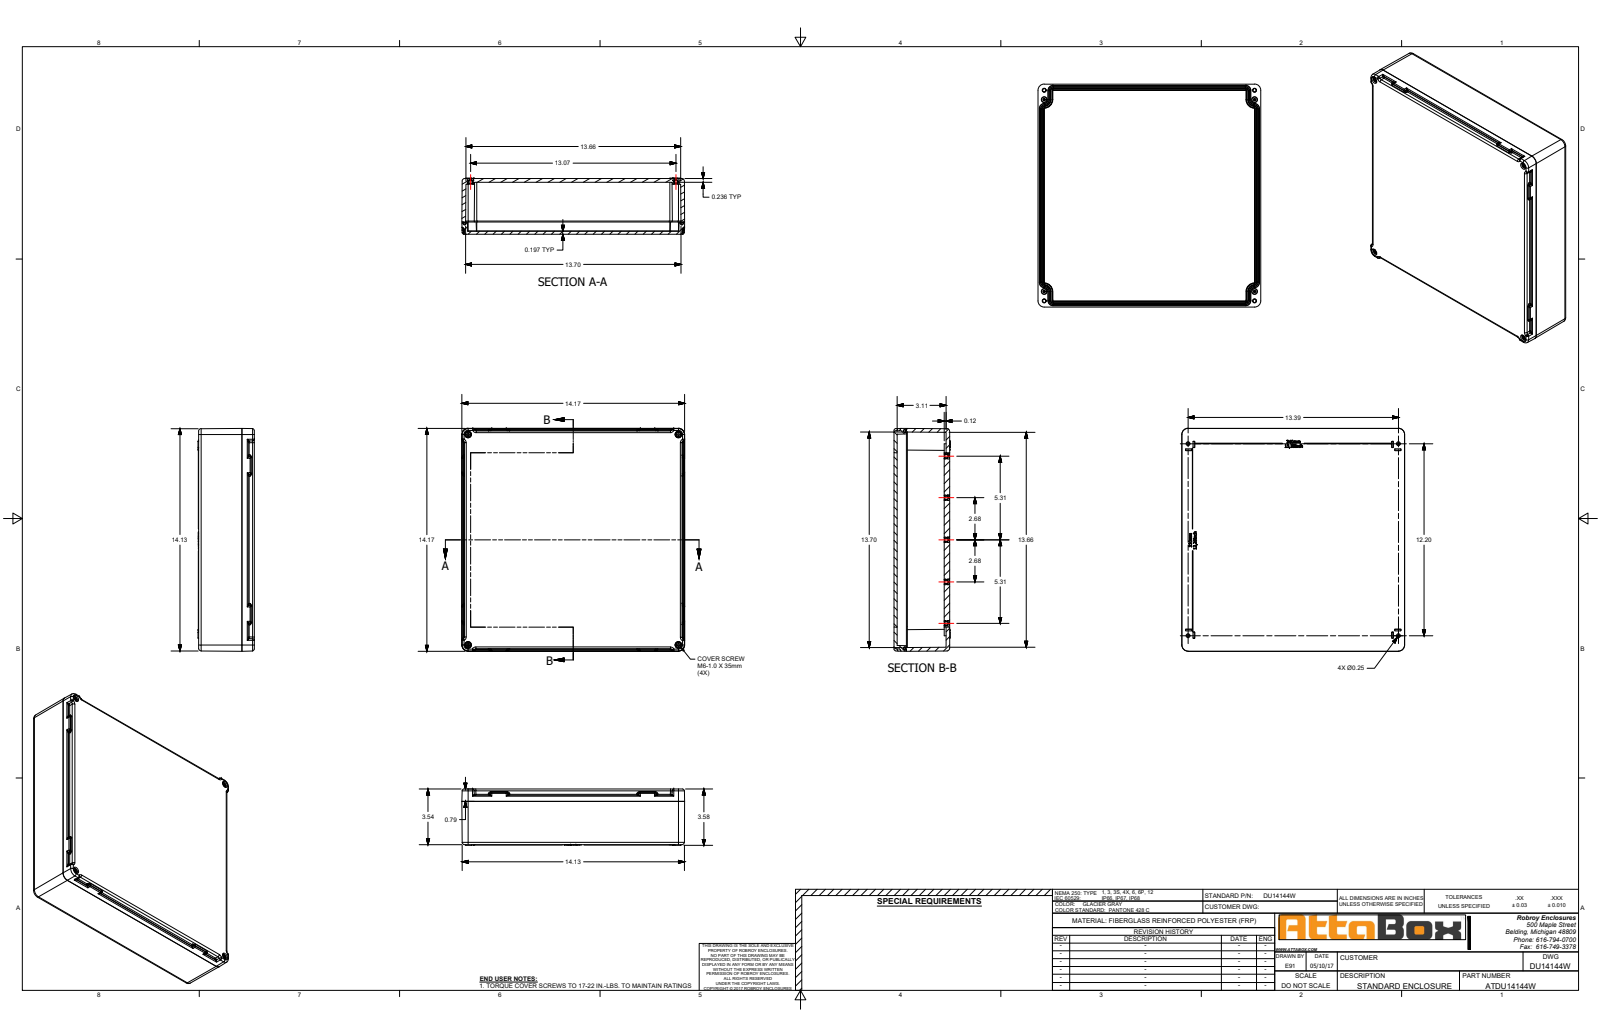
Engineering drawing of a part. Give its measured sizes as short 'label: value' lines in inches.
name: DU14144W
written by: SolidWorks 2018 (AUTOMOTIVE_DESIGN)
unit: in
bodies: 21 solids, 1677 faces (733 planar, 254 cylindrical, 690 other)
size: 14.173 × 14.173 × 3.583
volume: 135.1 in³; area: 1 276 in²
holes: 14× ⌀0.194, 10× ⌀0.236, 4× ⌀0.213, 4× ⌀0.276
bosses: 14× ⌀0.291, 4× ⌀0.374, 4× ⌀0.315, 4× ⌀0.236, 4× ⌀0.205
rounds: 32× R0.02, 24× R0.118, 16× R0.059, 12× R0.089, 8× R0.118, 8× R0.167, 8× R0.344, 6× R0.016
face distances: 0.236, 3.543, 0.197, 3.346, 3.307, 3.11, 0.787, 0.591, 2.52, 2.756
hole spacings: 13.071, 1.387, 2.638, 2.677, 4.019, 5.315, 6.695, 7.992
